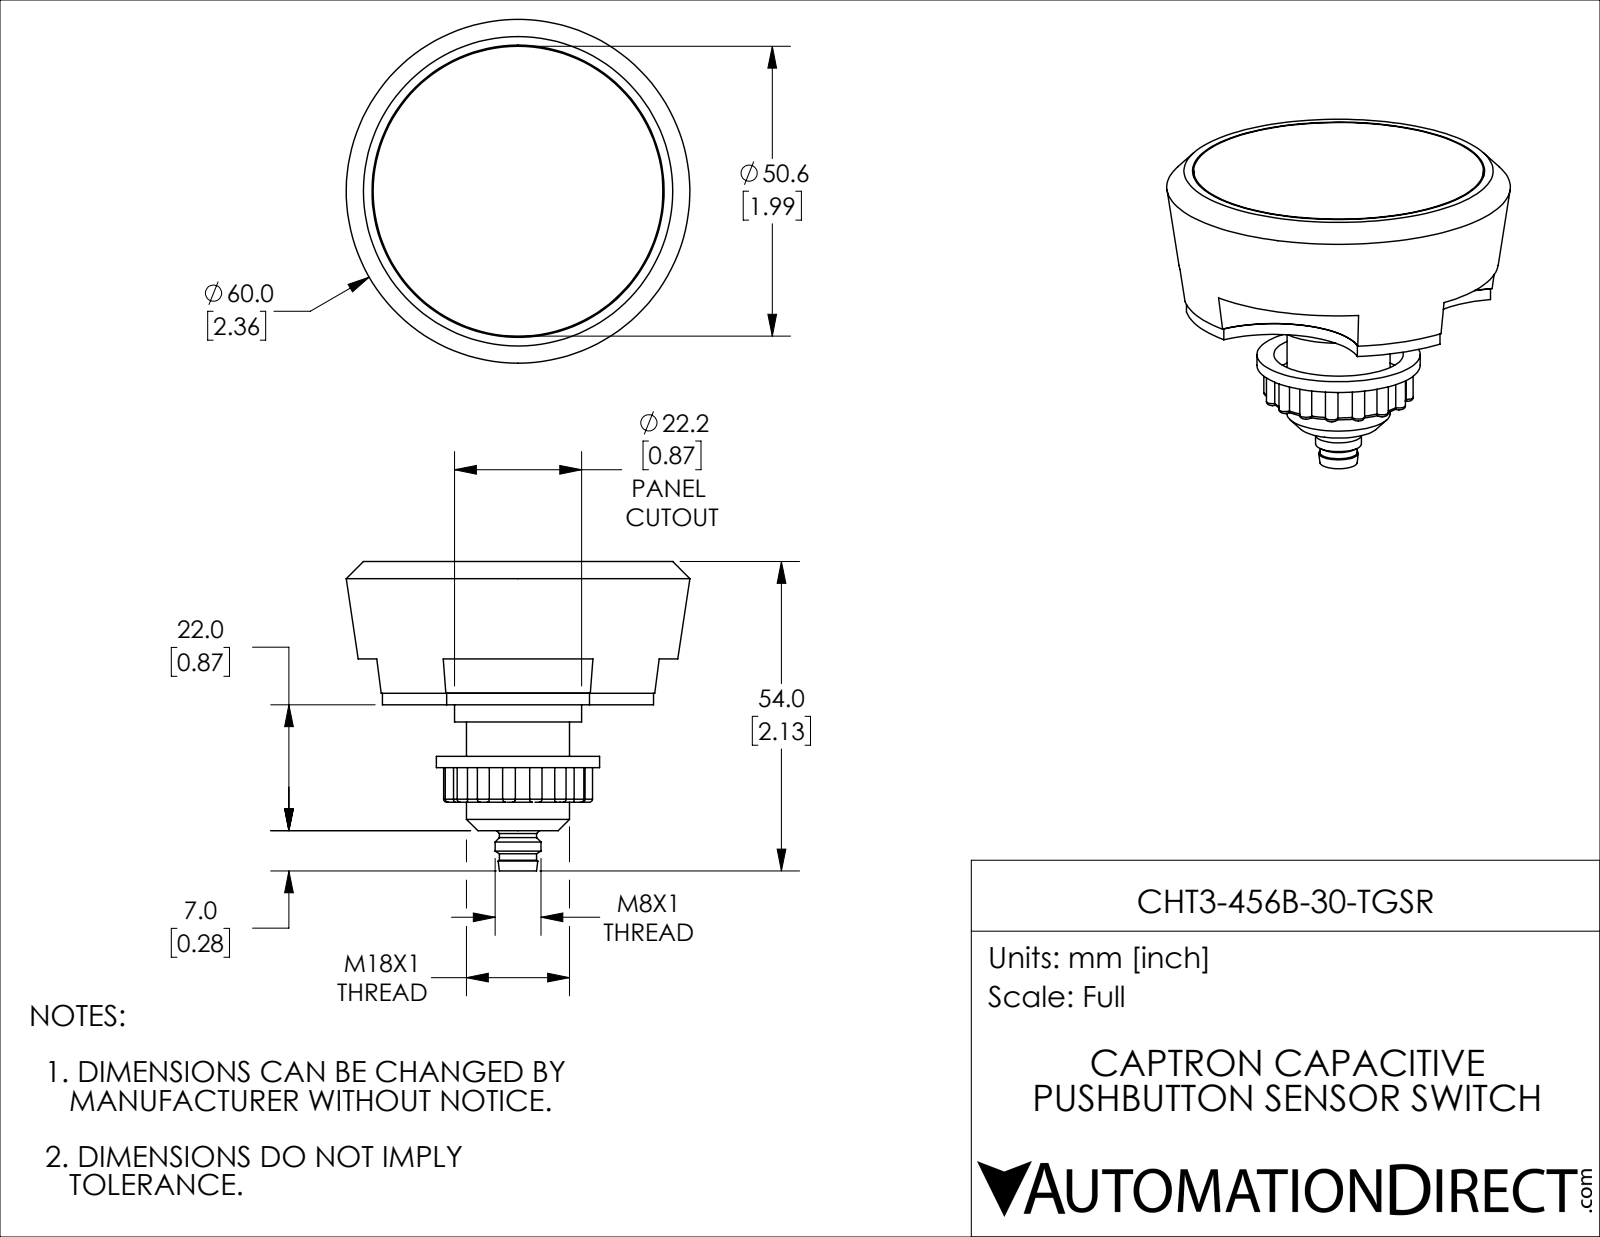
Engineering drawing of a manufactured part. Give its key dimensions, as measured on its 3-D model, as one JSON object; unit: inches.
{"part_name": "CHT3-456B-30-TGSR", "step_written_by": "SolidWorks 2019 (CONFIG_CONTROL_DESIGN)", "units": "inches", "bodies": {"solids": 10, "faces": 200, "planar": 28, "cylindrical": 94, "other": 78}, "overall_size": [2.362, 2.362, 2.126], "volume_in3": 3.853, "surface_area_in2": 32.45, "round_holes": [[0.669, 1], [0.89, 1], [2.008, 1]], "round_bosses_or_shafts": [[0.039, 5], [1.992, 1], [1.122, 1], [0.874, 1], [0.709, 1], [0.315, 1], [0.256, 1]], "partial_cylinders_radius": [[0.043, 16], [0.591, 4], [0.02, 2], [0.039, 1], [0.114, 1], [0.472, 1], [1.053, 1]], "face_to_face_distances": [0.906, 0.091, 0.815, 0.134, 0.772, 0.043, 0.079, 0.984, 0.669, 0.85]}
